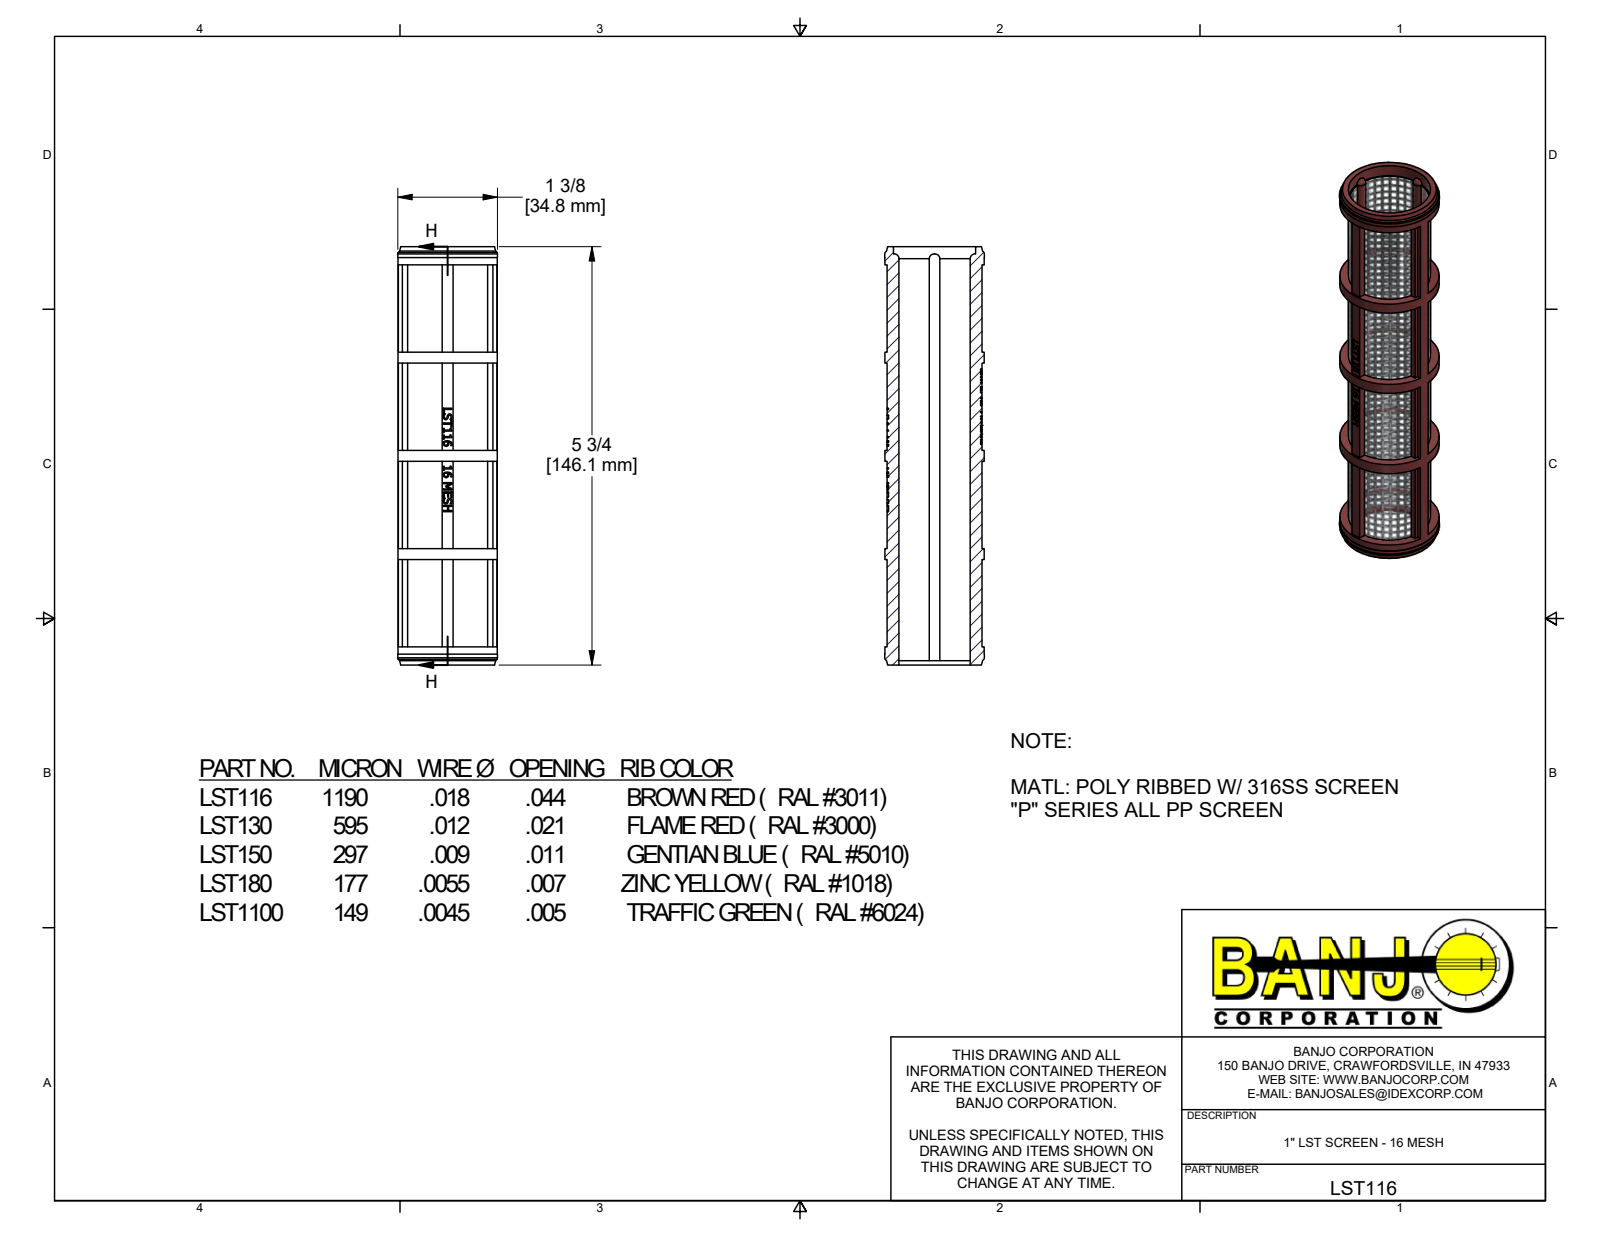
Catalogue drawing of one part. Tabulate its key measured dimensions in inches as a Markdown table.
| quantity | value |
| --- | --- |
| part name | LST116 |
| STEP written by | Autodesk Inventor 2019 (AUTOMOTIVE_DESIGN) |
| units | inches |
| bodies | 1 solid, 476 faces (356 planar, 29 cylindrical, 91 other) |
| overall size | 5.75 × 1.37 × 1.37 |
| volume | 1.229 in³ |
| surface area | 50.83 in² |
| round holes (diameter × count) | 0.98 × 1, 1.1 × 1 |
| round bosses / shafts (diameter × count) | 1.37 × 1, 1.365 × 1, 1.13 × 1 |
| partial cylindrical surfaces (radius × count) | 0.075 × 4 |
| main face-to-face distances | 1.35, 0.15, 1.2, 2.7, 0.528, 0.777, 2.55, 0.698, 0.547, 0.578 |
